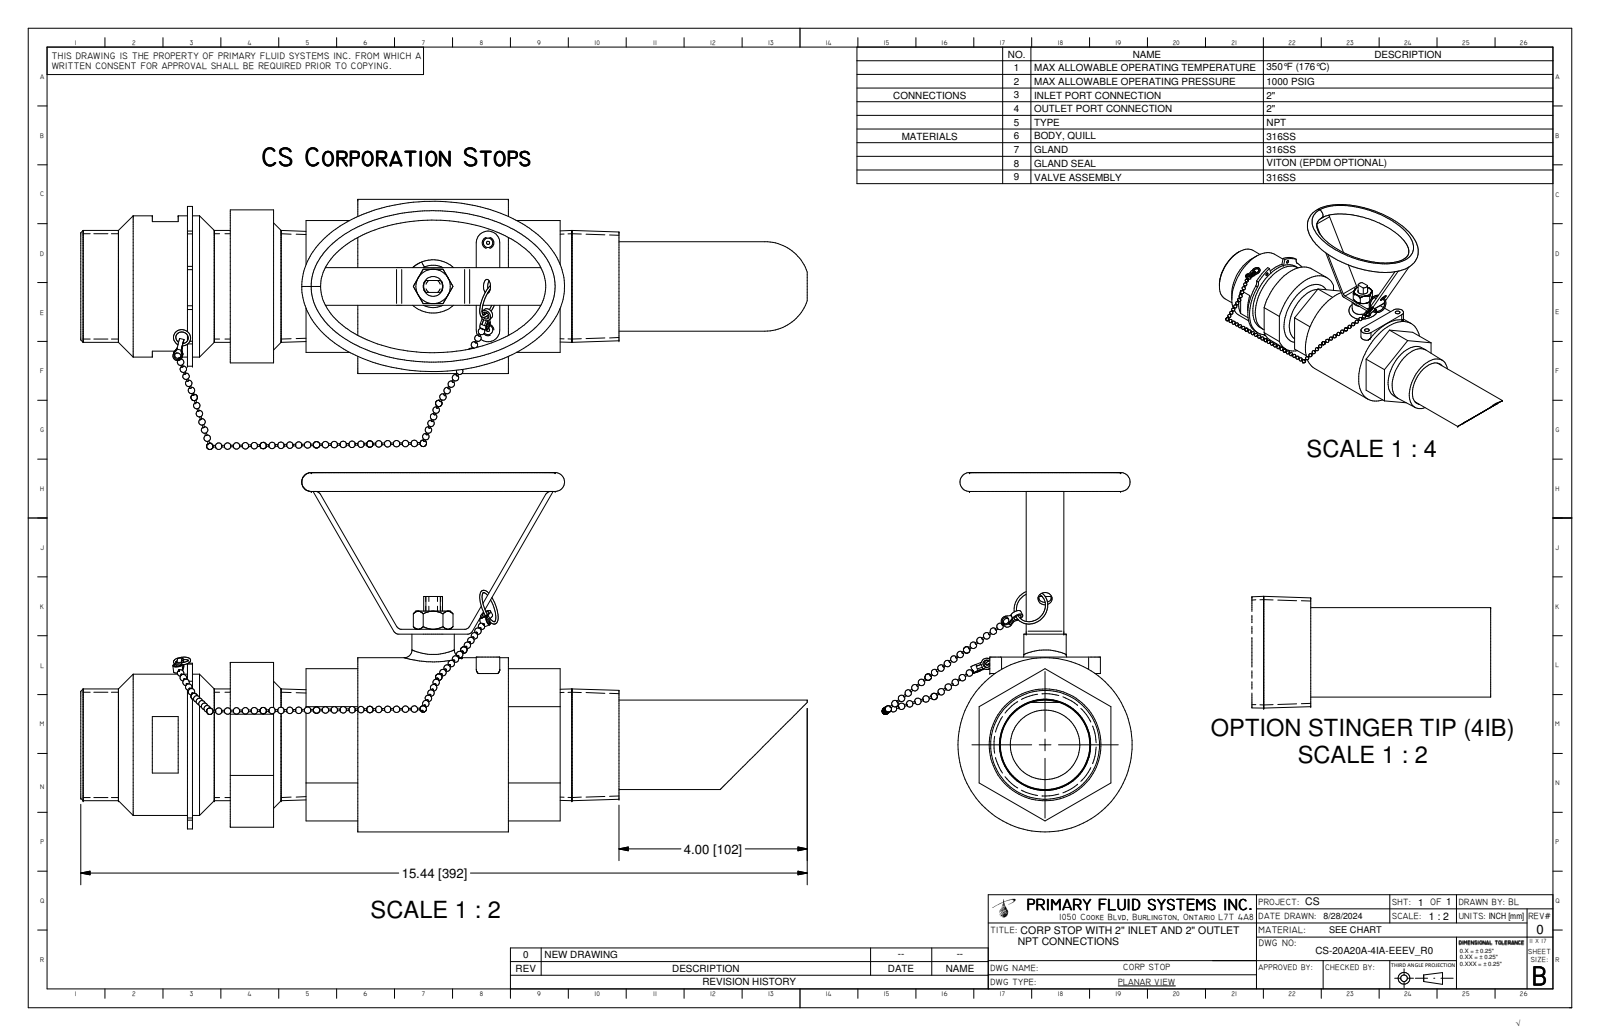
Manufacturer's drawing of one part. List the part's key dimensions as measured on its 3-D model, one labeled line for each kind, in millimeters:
STEP written by: Autodesk Inventor 2025 (CONFIG_CONTROL_DESIGN)
Units: millimetres
Bodies: 22 solids, 331 faces (126 planar, 113 cylindrical, 92 other)
Overall size (bounding box): 392.1 × 193.8 × 135
Volume: 1 121 000 mm³ · Surface area: 270 100 mm²
Round holes (diameter × count): ⌀1.7 ×2, ⌀3 ×2, ⌀3.8 ×2, ⌀4 ×2, ⌀5.1 ×2, ⌀7.6 ×1, ⌀10.7 ×1, ⌀37.5 ×1, ⌀38.1 ×1, ⌀49 ×1, ⌀49.3 ×1, ⌀50.8 ×1
Round bosses / shafts (diameter × count): ⌀0.9 ×9, ⌀6 ×2, ⌀94 ×1, ⌀76.2 ×1, ⌀69.1 ×1, ⌀60.3 ×1, ⌀57.3 ×1, ⌀52.9 ×1
Partial cylindrical surfaces — rounded edges, fillets, slot ends (radius × count): R3.2 ×8, R1.5 ×2, R2.5 ×2, R6 ×2, R6.4 ×2, R5.1 ×1, R43.1 ×1, R44.5 ×1
Main face-to-face distances: 71.1, 109.2, 27.9, 2.6, 178.1, 68.9, 150.1, 81.3, 23.4, 45.5
Hole centre spacings: 41.6, 31.5, 37.8, 37.8, 47
